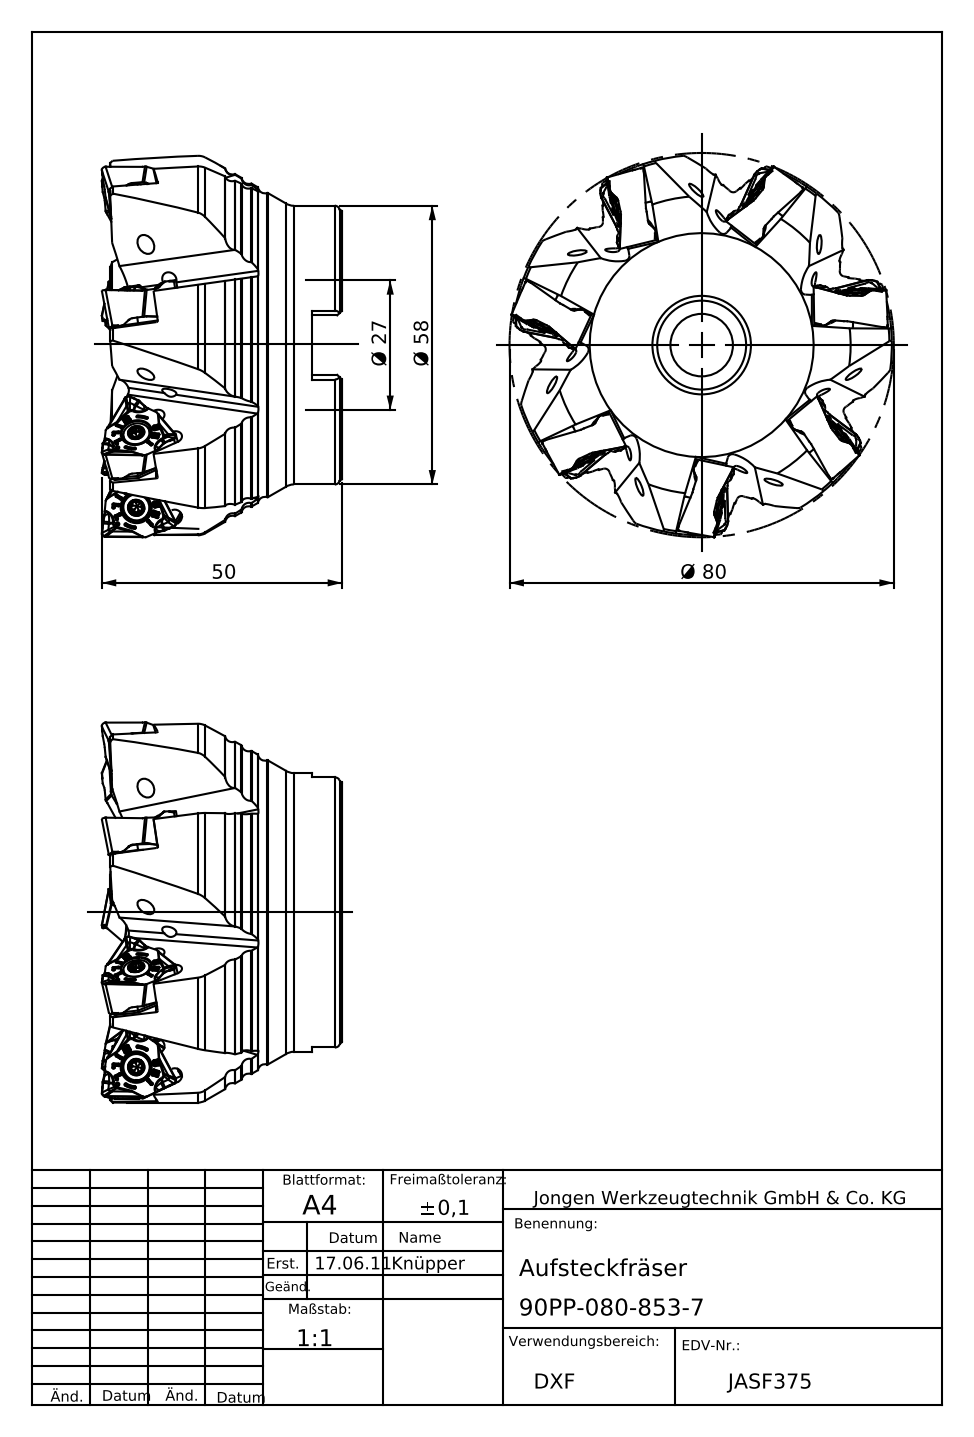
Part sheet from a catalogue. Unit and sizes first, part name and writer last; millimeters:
Units: millimetres
Overall size (bounding box): 80 × 80 × 50.05
Round holes (diameter × count): ⌀3 ×7, ⌀13 ×1, ⌀18.5 ×1, ⌀27 ×1, ⌀27.15 ×1, ⌀27.3 ×1
Round bosses / shafts (diameter × count): ⌀80 ×1, ⌀79.15 ×1, ⌀58 ×1
Partial cylindrical surfaces — rounded edges, fillets, slot ends (radius × count): R0.3 ×14, R1.5 ×14
Main face-to-face distances: 48.2, 44.25, 3.95, 7, 37.25, 41.2, 25.05, 18.05, 19.2, 23.15
Volume: 157 417 mm³ · Surface area: 28 238 mm²
Bodies: 1 solid, 360 faces (69 planar, 81 cylindrical, 210 other)
Part name (STEP PRODUCT): 90PP-080-853-7
STEP written by: SolidWorks 2010 (AUTOMOTIVE_DESIGN)
